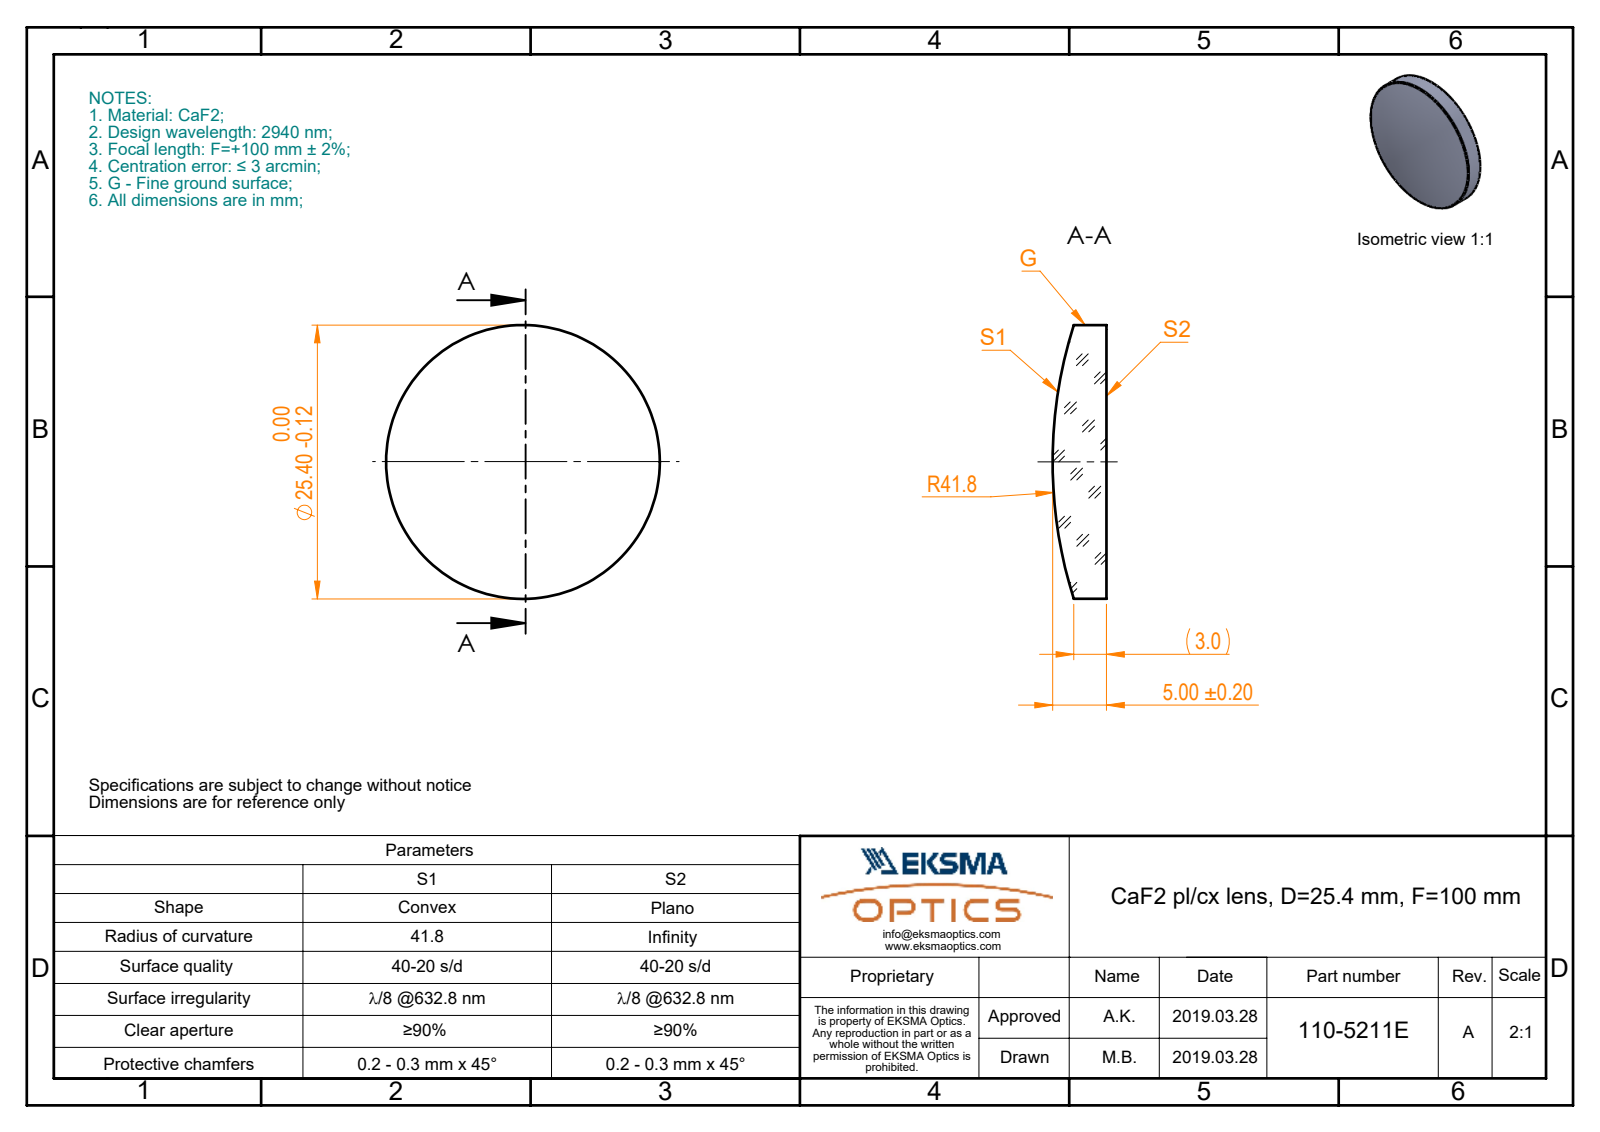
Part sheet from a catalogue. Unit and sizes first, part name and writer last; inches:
Units: inches
Overall size (bounding box): 1 × 1 × 0.197
Round bosses / shafts (diameter × count): ⌀1 ×1
Volume: 0.124 in³ · Surface area: 1.964 in²
Bodies: 1 solid, 5 faces (1 planar, 2 cylindrical, 2 other)
Part name (STEP PRODUCT): 110-5211E CaF2 pl-cx 25.4 F100
STEP written by: SolidWorks 2017 (CONFIG_CONTROL_DESIGN)
